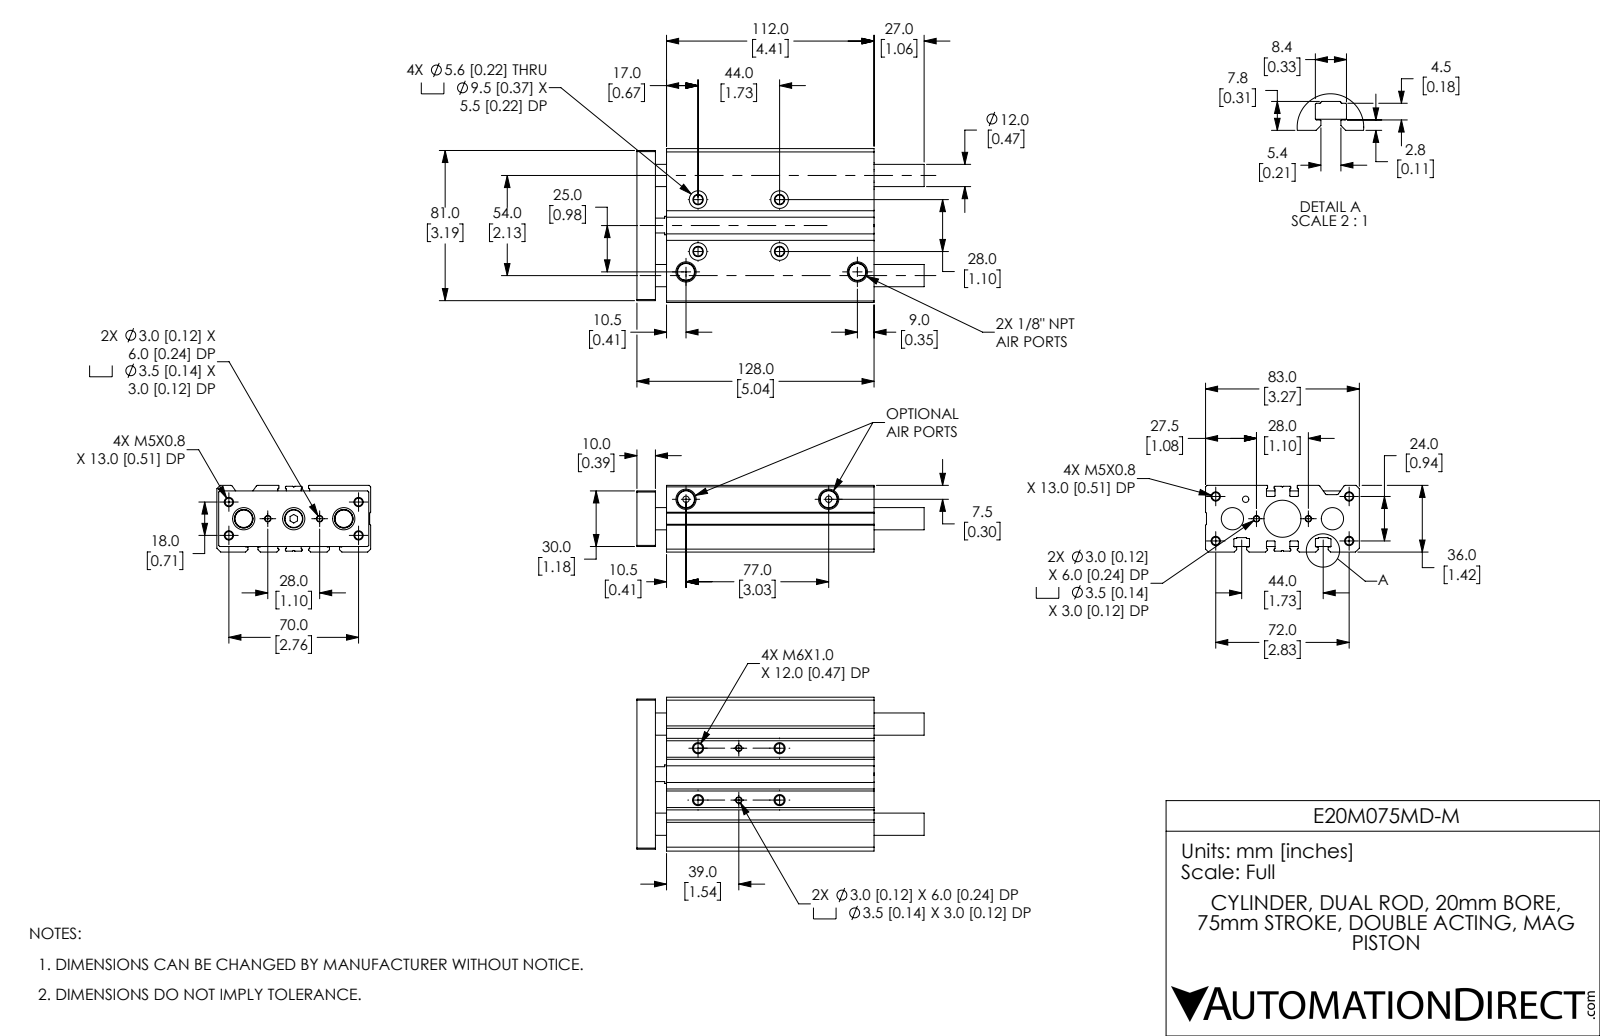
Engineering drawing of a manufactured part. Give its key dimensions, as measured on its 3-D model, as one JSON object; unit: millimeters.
{"part_name": "E20M075MD-M; E20M075MD-M_BODY; E20M075MD-M_ENDPLATE", "step_written_by": "SolidWorks 2019 (CONFIG_CONTROL_DESIGN)", "units": "millimeters", "bodies": {"solids": 5, "faces": 404, "planar": 128, "cylindrical": 182, "other": 94}, "overall_size": [155, 83, 36], "volume_mm3": 307087, "surface_area_mm2": 87956, "round_holes": [[4.13, 8], [3, 4], [3.5, 4], [4.92, 4], [5.6, 4], [9.5, 4], [6, 3], [12, 3], [3.43, 2], [9.91, 2], [3.43, 1], [12, 1]], "round_bosses_or_shafts": [[10, 1], [9.91, 1]], "partial_cylinders_radius": [[0.4, 20], [0.2, 18], [0.3, 10], [0.25, 8], [1, 4]], "face_to_face_distances": [36, 6, 3, 0.5, 83, 30, 16, 128, 112, 10], "hole_center_spacings": [3.16, 12.04, 15, 21.02, 22, 22.85, 25.06, 28]}
